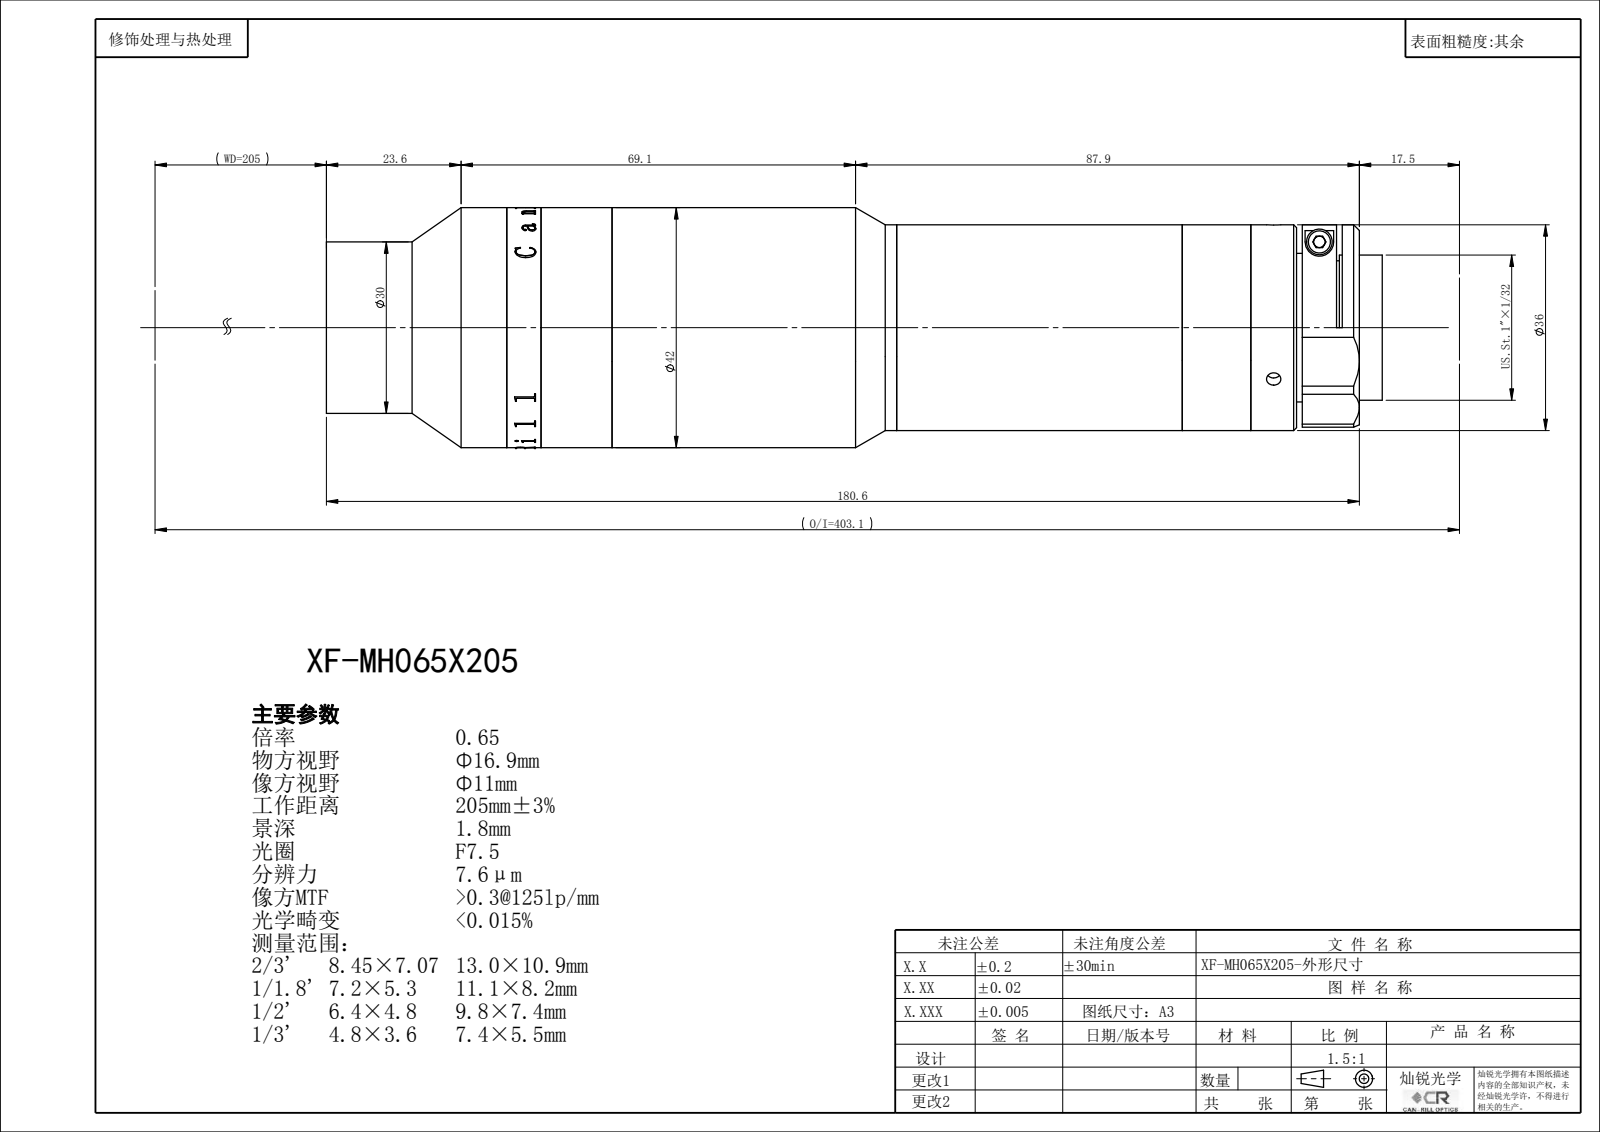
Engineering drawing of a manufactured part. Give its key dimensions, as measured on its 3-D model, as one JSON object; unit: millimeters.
{"part_name": "XF-MH065X205", "step_written_by": "SolidWorks 2022 (CONFIG_CONTROL_DESIGN)", "units": "millimeters", "bodies": {"solids": 0, "faces": 133, "planar": 67, "cylindrical": 42, "other": 24}, "overall_size": [184.49, 42, 42], "round_holes": [[2.5, 3], [22.4, 1], [24, 1], [26.4, 1]], "round_bosses_or_shafts": [[42, 1], [36, 1], [34, 1], [30, 1], [25.4, 1]], "face_to_face_distances": [18.66, 1.5, 17.16, 6, 62, 79.16, 80.66, 50, 99.83, 68]}
